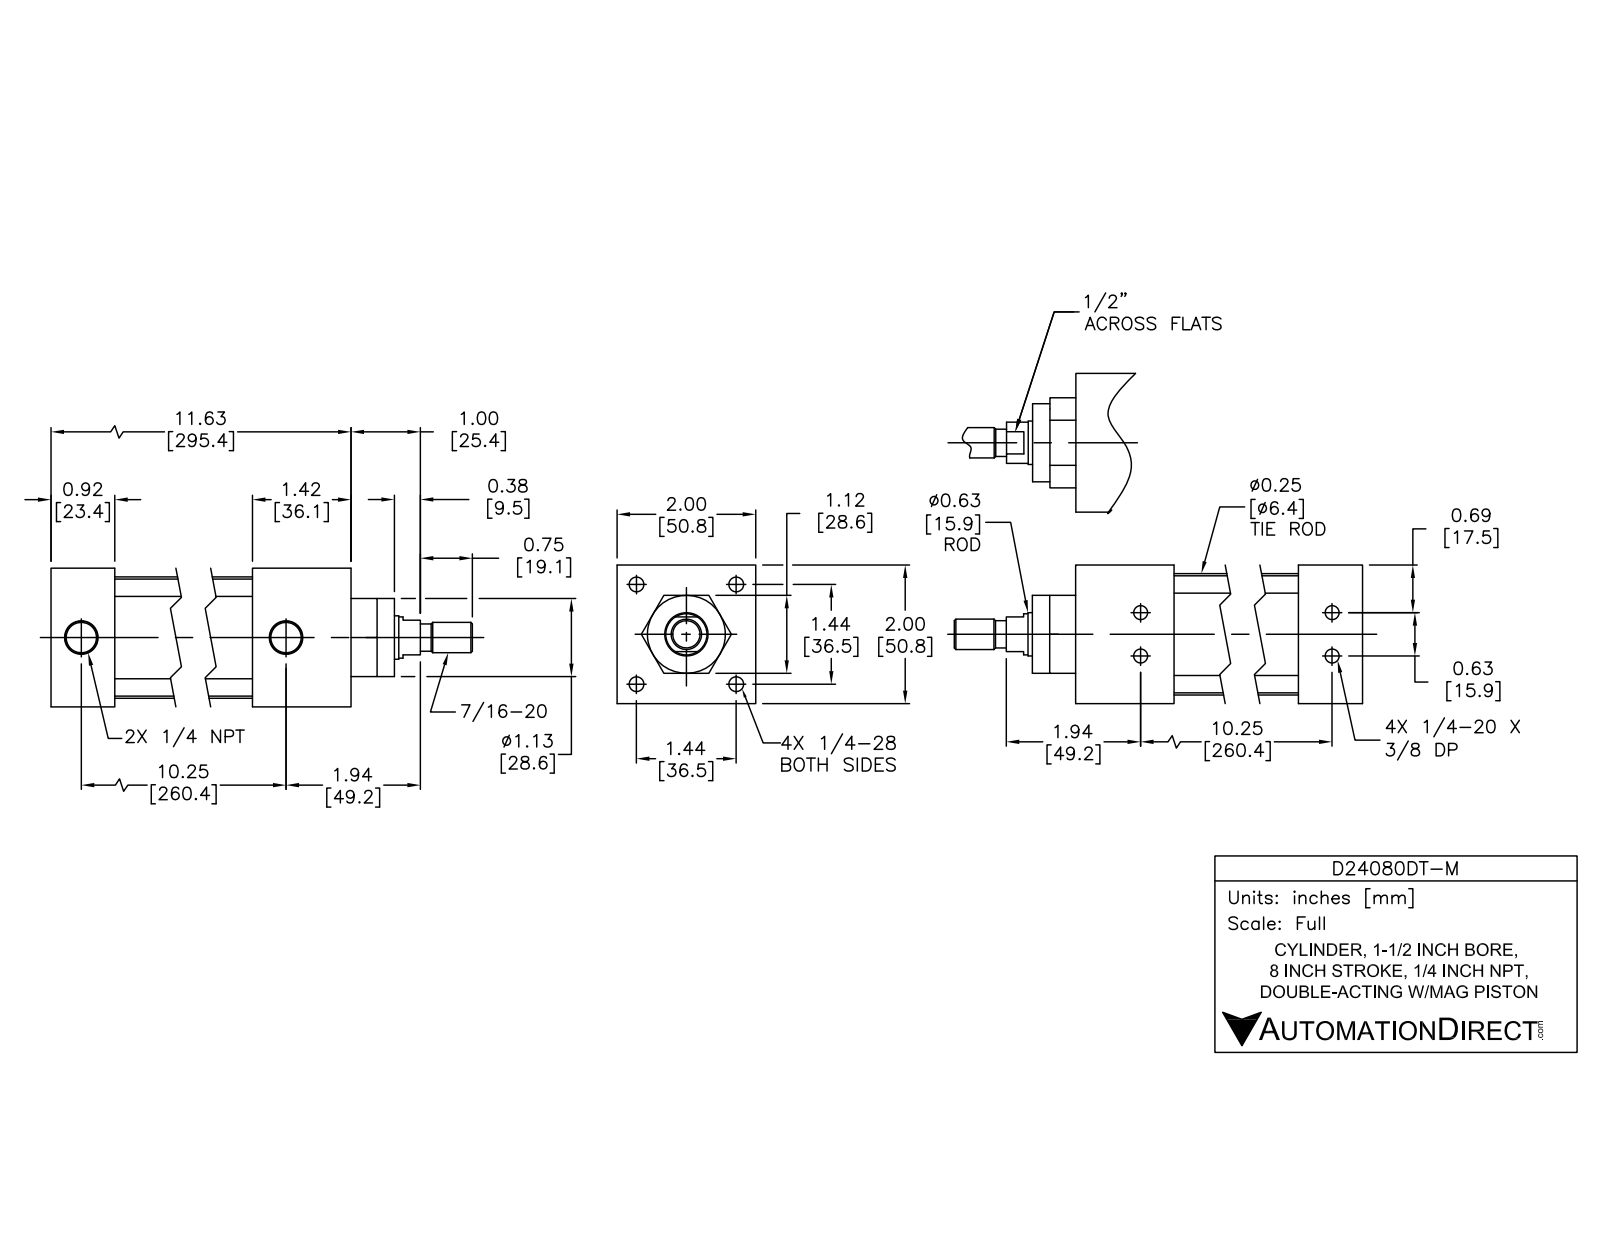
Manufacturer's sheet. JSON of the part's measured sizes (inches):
{"part_name": "D24080DT-M; D24080DT-M PISTON; D24080DT-M BODY", "step_written_by": "SolidWorks 2015 (AUTOMOTIVE_DESIGN)", "units": "inches", "bodies": {"solids": 12, "faces": 303, "planar": 99, "cylindrical": 114, "other": 90}, "overall_size": [13.371, 2, 2], "volume_in3": 21.46, "surface_area_in2": 212.7, "round_holes": [[0.196, 4], [0.211, 4], [0.281, 4], [0.406, 4], [0.297, 2], [0.477, 2], [0.625, 1], [0.628, 1], [1.5, 1]], "round_bosses_or_shafts": [[0.39, 4], [0.25, 4], [0.222, 4], [1.75, 1], [1.497, 1], [1.121, 1], [0.622, 1], [0.59, 1]], "partial_cylinders_radius": [[0.2, 4]], "face_to_face_distances": [2, 0.08, 9.201, 11.621, 1.42, 10.201, 10.701, 9.281, 0.92, 1.121], "hole_center_spacings": [1.434, 10.251, 0.312, 0.313, 0.625, 1.014, 2.028, 10.247]}
